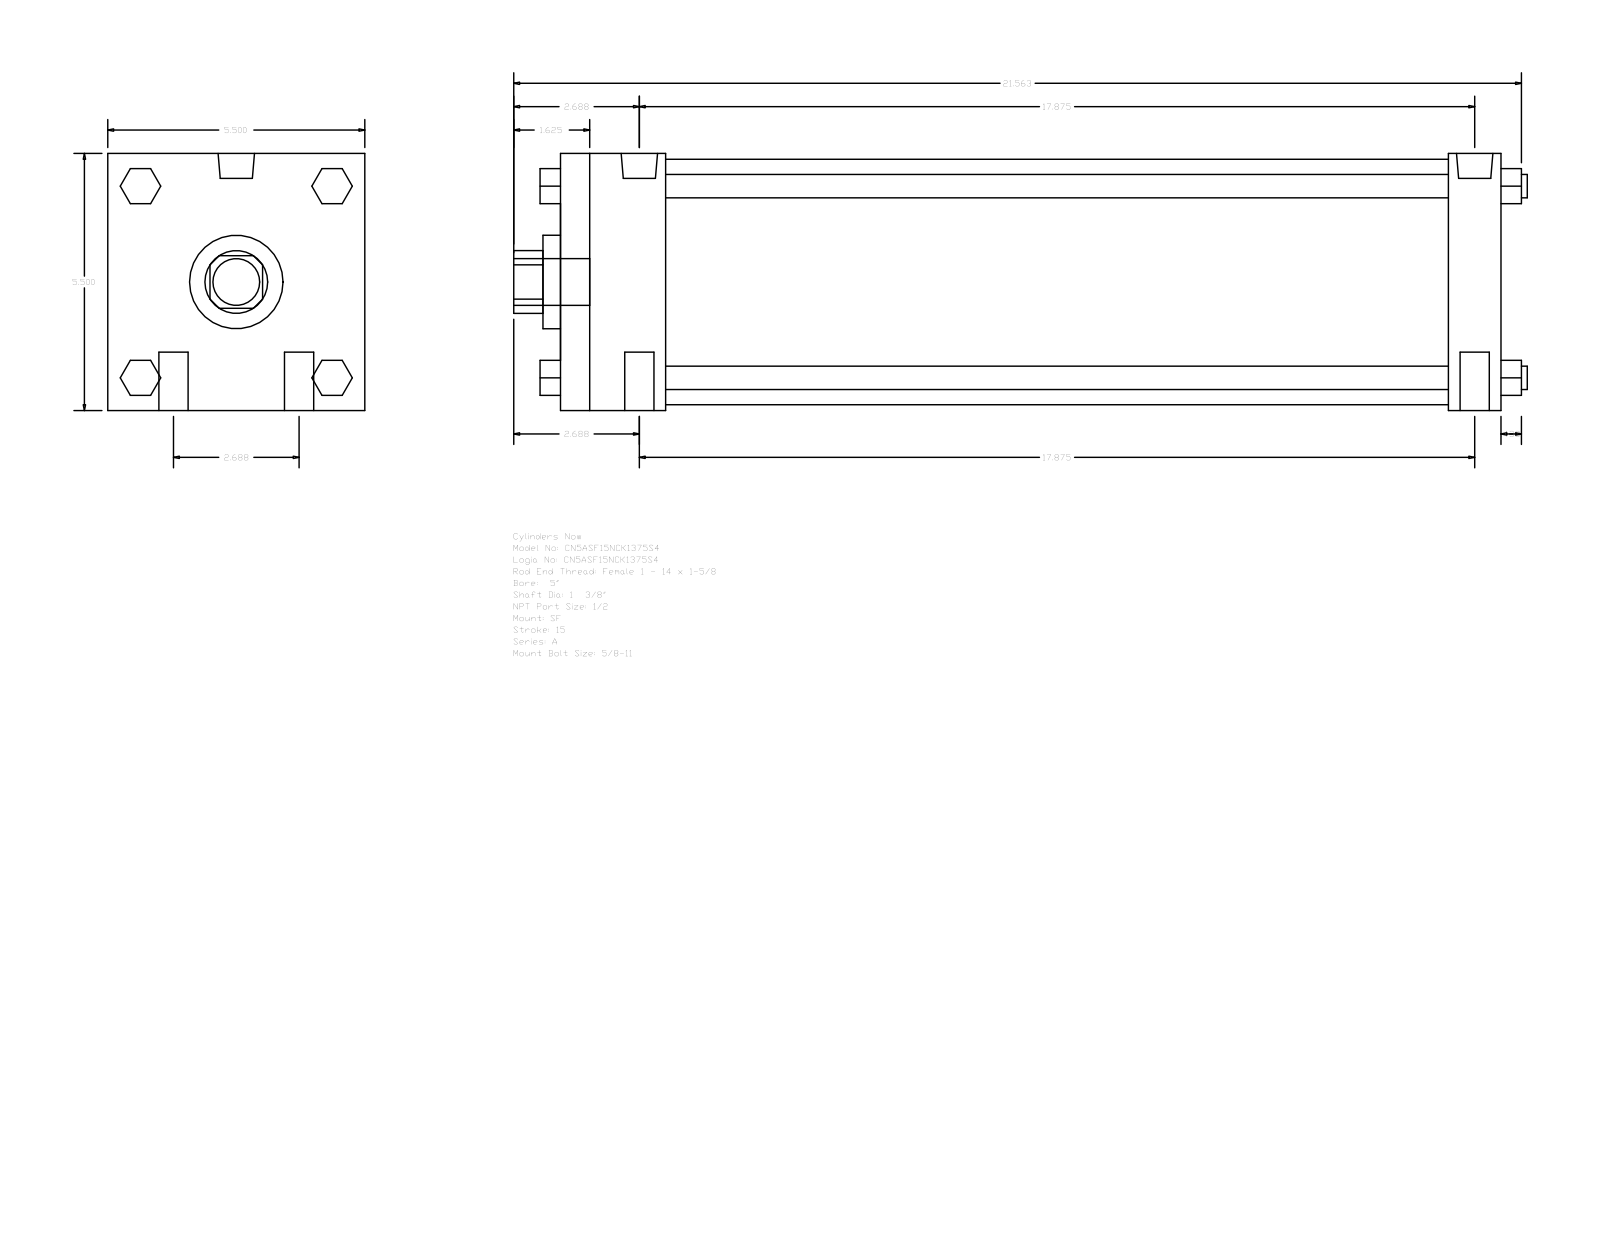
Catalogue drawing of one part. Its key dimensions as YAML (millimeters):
part_name: "A_SF__0500_1.375"
step_written_by: "GSSL Pune (CONFIG_CONTROL_DESIGN)"
units: millimeters
bodies: {solids: 0, faces: 124, planar: 94, cylindrical: 30, other: 0}
overall_size: [550.86, 139.7, 139.7]
round_holes:
  - {diameter: 34.92, count: 1}
  - {diameter: 50.8, count: 1}
  - {diameter: 133.35, count: 1}
round_bosses_or_shafts:
  - {diameter: 15.88, count: 4}
  - {diameter: 12.7, count: 4}
  - {diameter: 19.77, count: 2}
  - {diameter: 8.73, count: 2}
  - {diameter: 25.4, count: 1}
partial_cylinders:
  - {radius: 17.06, count: 1}
face_to_face_distances: [139.7, 511.18, 28.58, 57.15, 482.6, 425.45, 454.03, 19.05, 52.07, 90.18]
